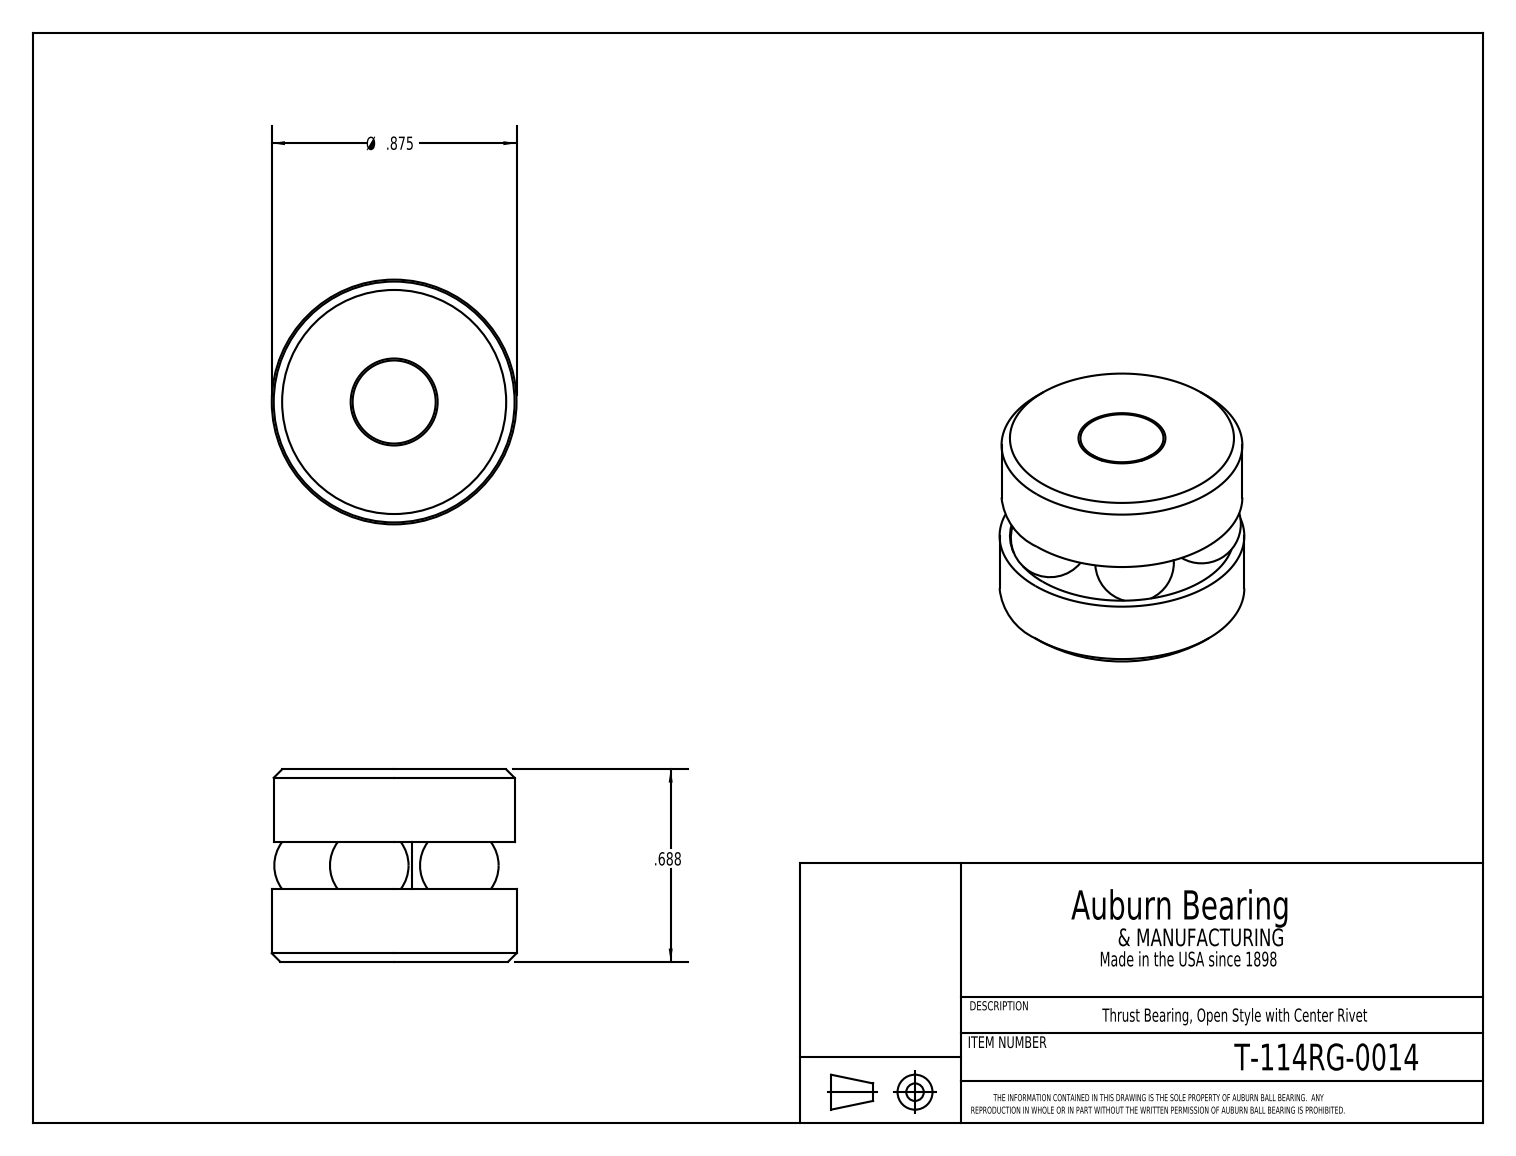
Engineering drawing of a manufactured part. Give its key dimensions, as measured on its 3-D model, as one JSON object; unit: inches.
{"part_name": "T-114RG_T-114RG-0014", "step_written_by": "SolidWorks 2016 (CONFIG_CONTROL_DESIGN)", "units": "inches", "bodies": {"solids": 8, "faces": 26, "planar": 8, "cylindrical": 5, "other": 13}, "overall_size": [0.875, 0.875, 0.688], "volume_in3": 0.331, "surface_area_in2": 5.695, "round_holes": [[0.135, 1]], "round_bosses_or_shafts": [[0.875, 1], [0.861, 1], [0.125, 1]], "face_to_face_distances": [0.687, 0.259, 0.428, 0.169]}
